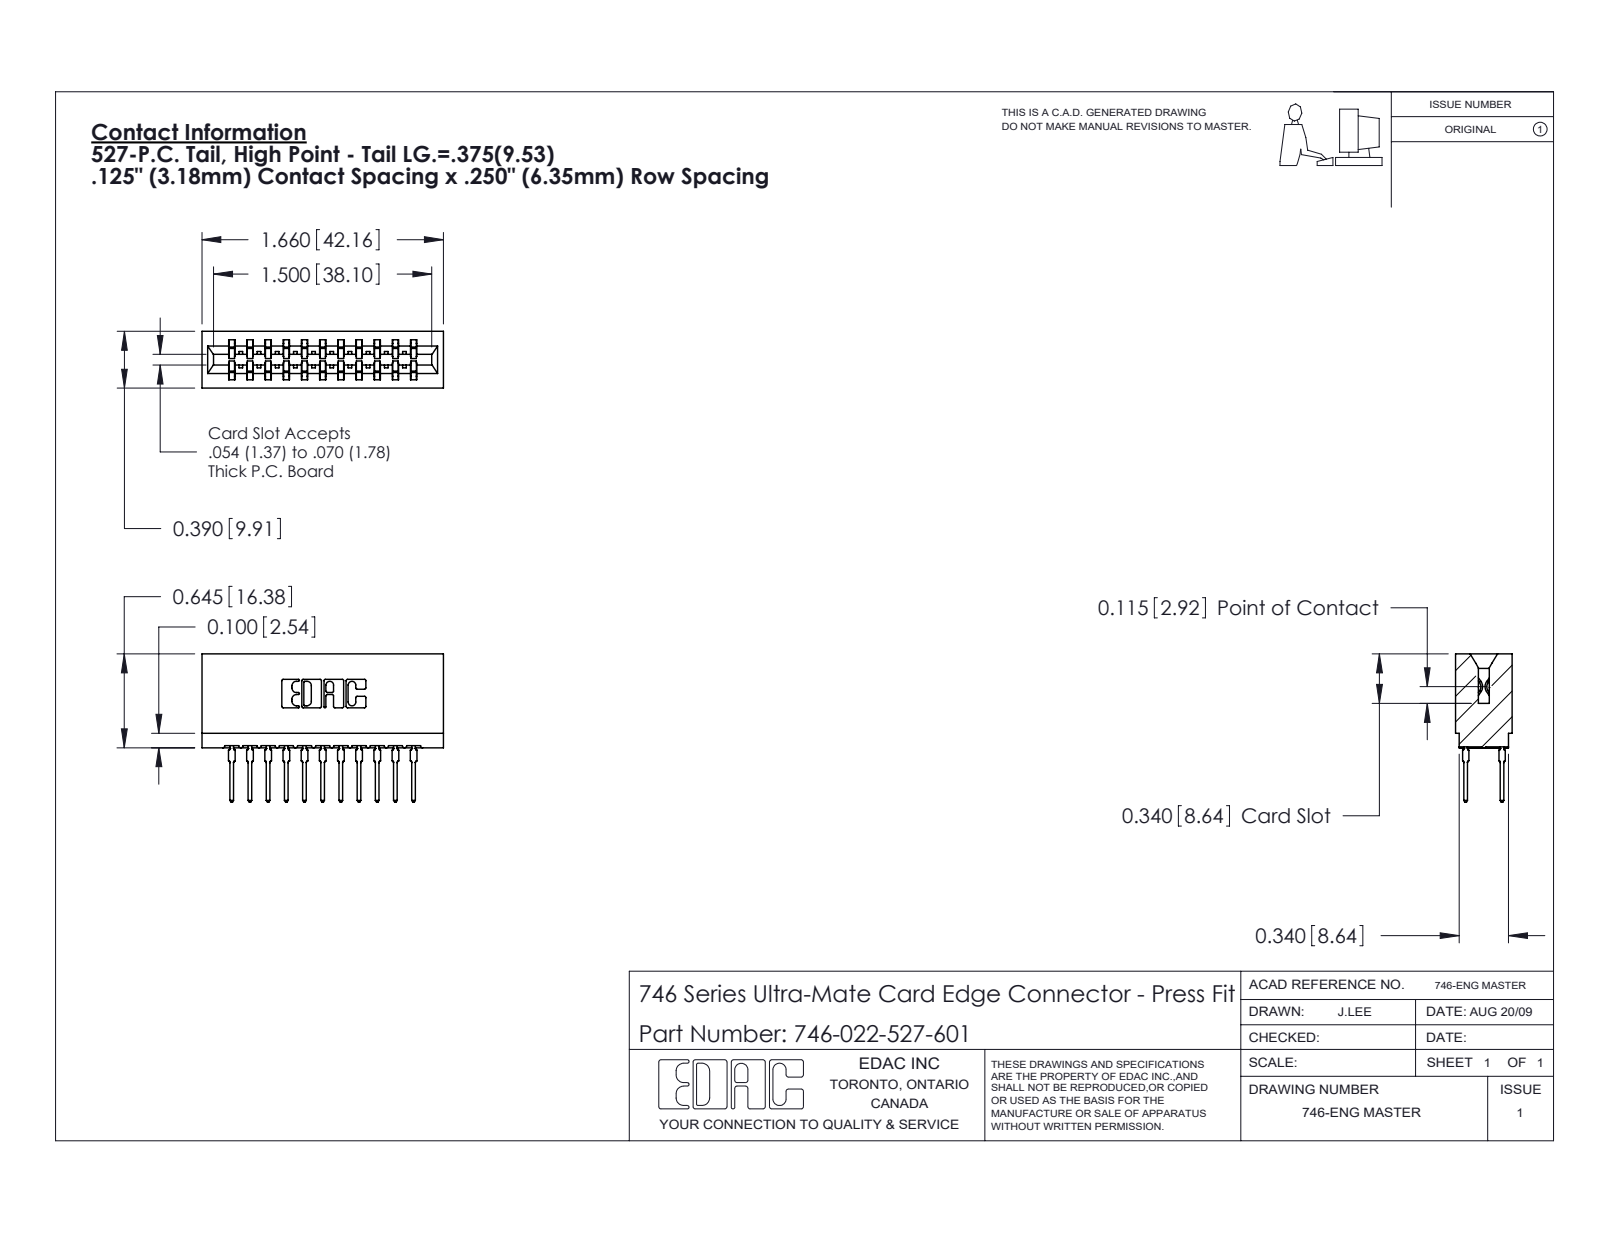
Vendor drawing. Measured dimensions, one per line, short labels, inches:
name: 746 Part_.340 Slot Depth - 01; 746-292-001_527; 746-022-527-601
written by: SolidWorks 2020 (CONFIG_CONTROL_DESIGN)
unit: in
bodies: 23 solids, 2066 faces (1067 planar, 427 cylindrical, 572 other)
size: 1.66 × 1.019 × 0.39
volume: 0.309 in³; area: 10.89 in²
rounds: 44× R0.021, 22× R0.01, 12× R0.015, 8× R0.005, 8× R0.011, 6× R0.007, 6× R0.031, 3× R0.026
face distances: 0.25, 0.057, 0.333, 0.5, 0.125, 0.292, 0.125, 0.042, 0.542, 0.39
